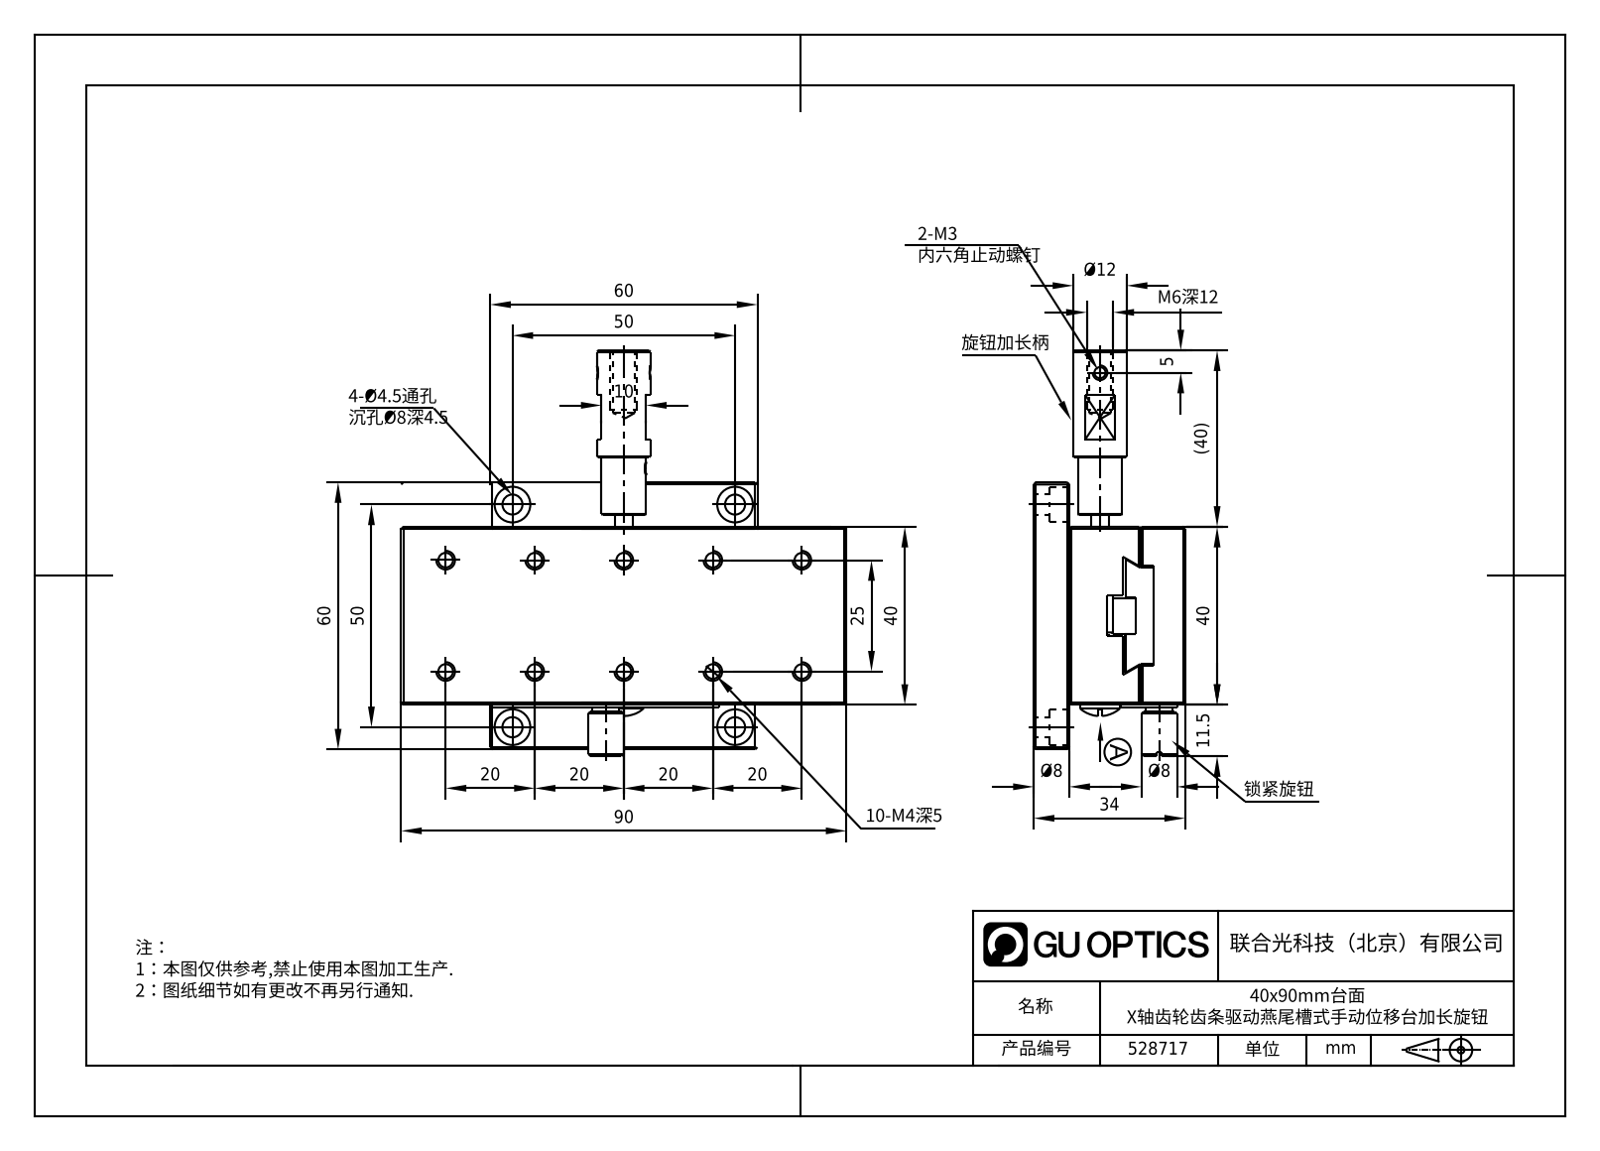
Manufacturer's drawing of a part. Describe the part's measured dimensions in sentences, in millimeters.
The part is named "528717". Its 3-D file was written by "SolidWorks 2020 (CONFIG_CONTROL_DESIGN)". It is 0 solids with 319 faces: 183 planar, 72 cylindrical and 64 other. Overall it measures 91.5 by 90 by 34 millimeters. Round holes: 12 of diameter 3.24, 6 of diameter 8, 5 of diameter 2.8, 5 of diameter 5, 4 of diameter 2.01, 4 of diameter 2.46, 4 of diameter 4.5, 2 of diameter 1.57, 2 of diameter 2.2, 2 of diameter 4.2, 1 of diameter 2.01, 1 of diameter 4. Round bosses or shafts: 2 of diameter 8, 1 of diameter 12, 1 of diameter 10, 1 of diameter 9, 1 of diameter 6.5, 1 of diameter 6, 1 of diameter 5.83, 1 of diameter 3.5. Partial cylindrical surfaces (rounded edges, fillets, slot ends): 4 of radius 2, 2 of radius 1.8. The main face-to-face distances are 7, 19, 34, 26, 8, 16, 24, 27, 10, 0.5. The hole center spacings are 20, 27.95, 32.02, 45.07, 25, 40, 47.17, 65.
